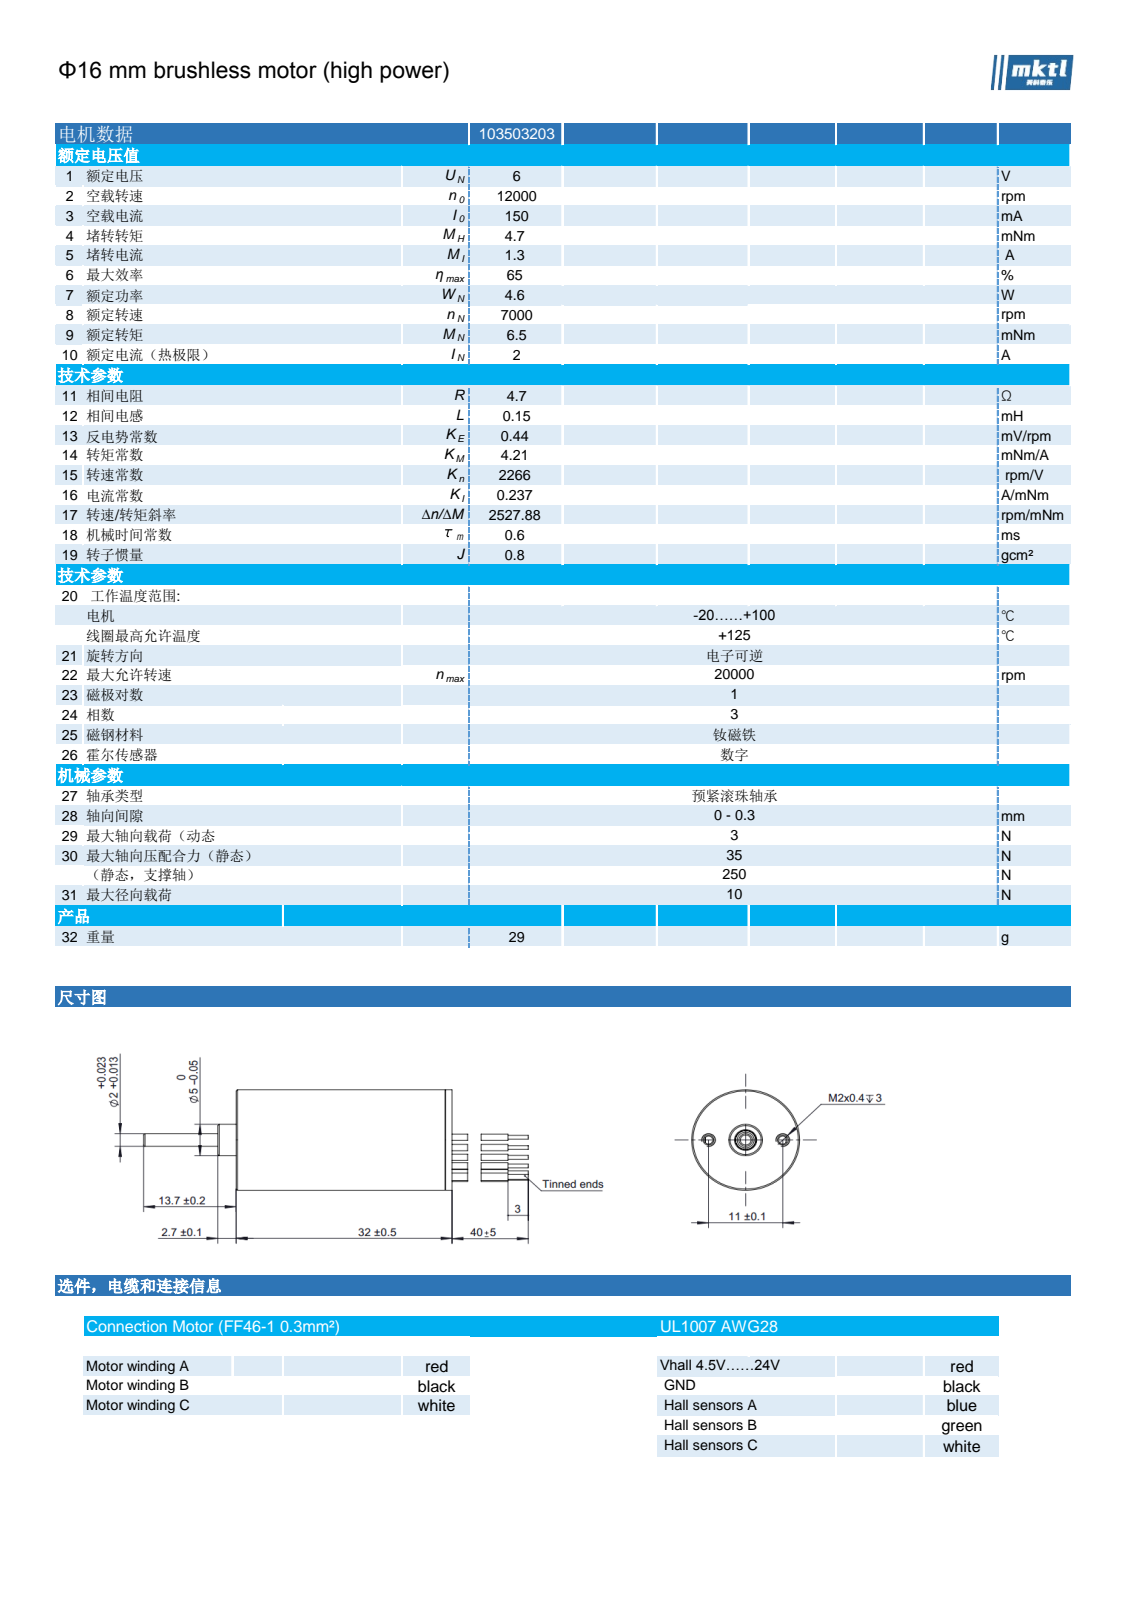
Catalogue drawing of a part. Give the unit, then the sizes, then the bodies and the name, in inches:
Units: inches
Overall size (bounding box): 2.244 × 0.63 × 0.63
Round holes (diameter × count): ⌀0.047 ×8, ⌀0.024 ×5, ⌀0.031 ×3, ⌀0.043 ×3, ⌀0.055 ×3, ⌀0.063 ×2, ⌀0.118 ×1, ⌀0.13 ×1, ⌀0.138 ×1, ⌀0.177 ×1, ⌀0.276 ×1, ⌀0.315 ×1
Round bosses / shafts (diameter × count): ⌀0.039 ×5, ⌀0.047 ×3, ⌀0.031 ×3, ⌀0.012 ×3, ⌀0.63 ×1, ⌀0.591 ×1, ⌀0.587 ×1, ⌀0.571 ×1
Partial cylindrical surfaces — rounded edges, fillets, slot ends (radius × count): R0.022 ×2, R0.033 ×2, R0.203 ×1, R0.222 ×1, R0.256 ×1, R0.27 ×1, R0.283 ×1
Main face-to-face distances: 0.016, 0.024, 0.039, 0.031, 0.047, 0.055, 0.063, 0.071, 0.079, 0.087
Hole centre spacings: 0.065, 0.128, 0.236, 0.247, 0.248, 0.268, 0.467, 0.056
Volume: 0.35 in³ · Surface area: 35.85 in²
Bodies: 130 solids, 991 faces (339 planar, 591 cylindrical, 61 other)
Part name (STEP PRODUCT): 103503203
STEP written by: SolidWorks 2025 (AUTOMOTIVE_DESIGN)
